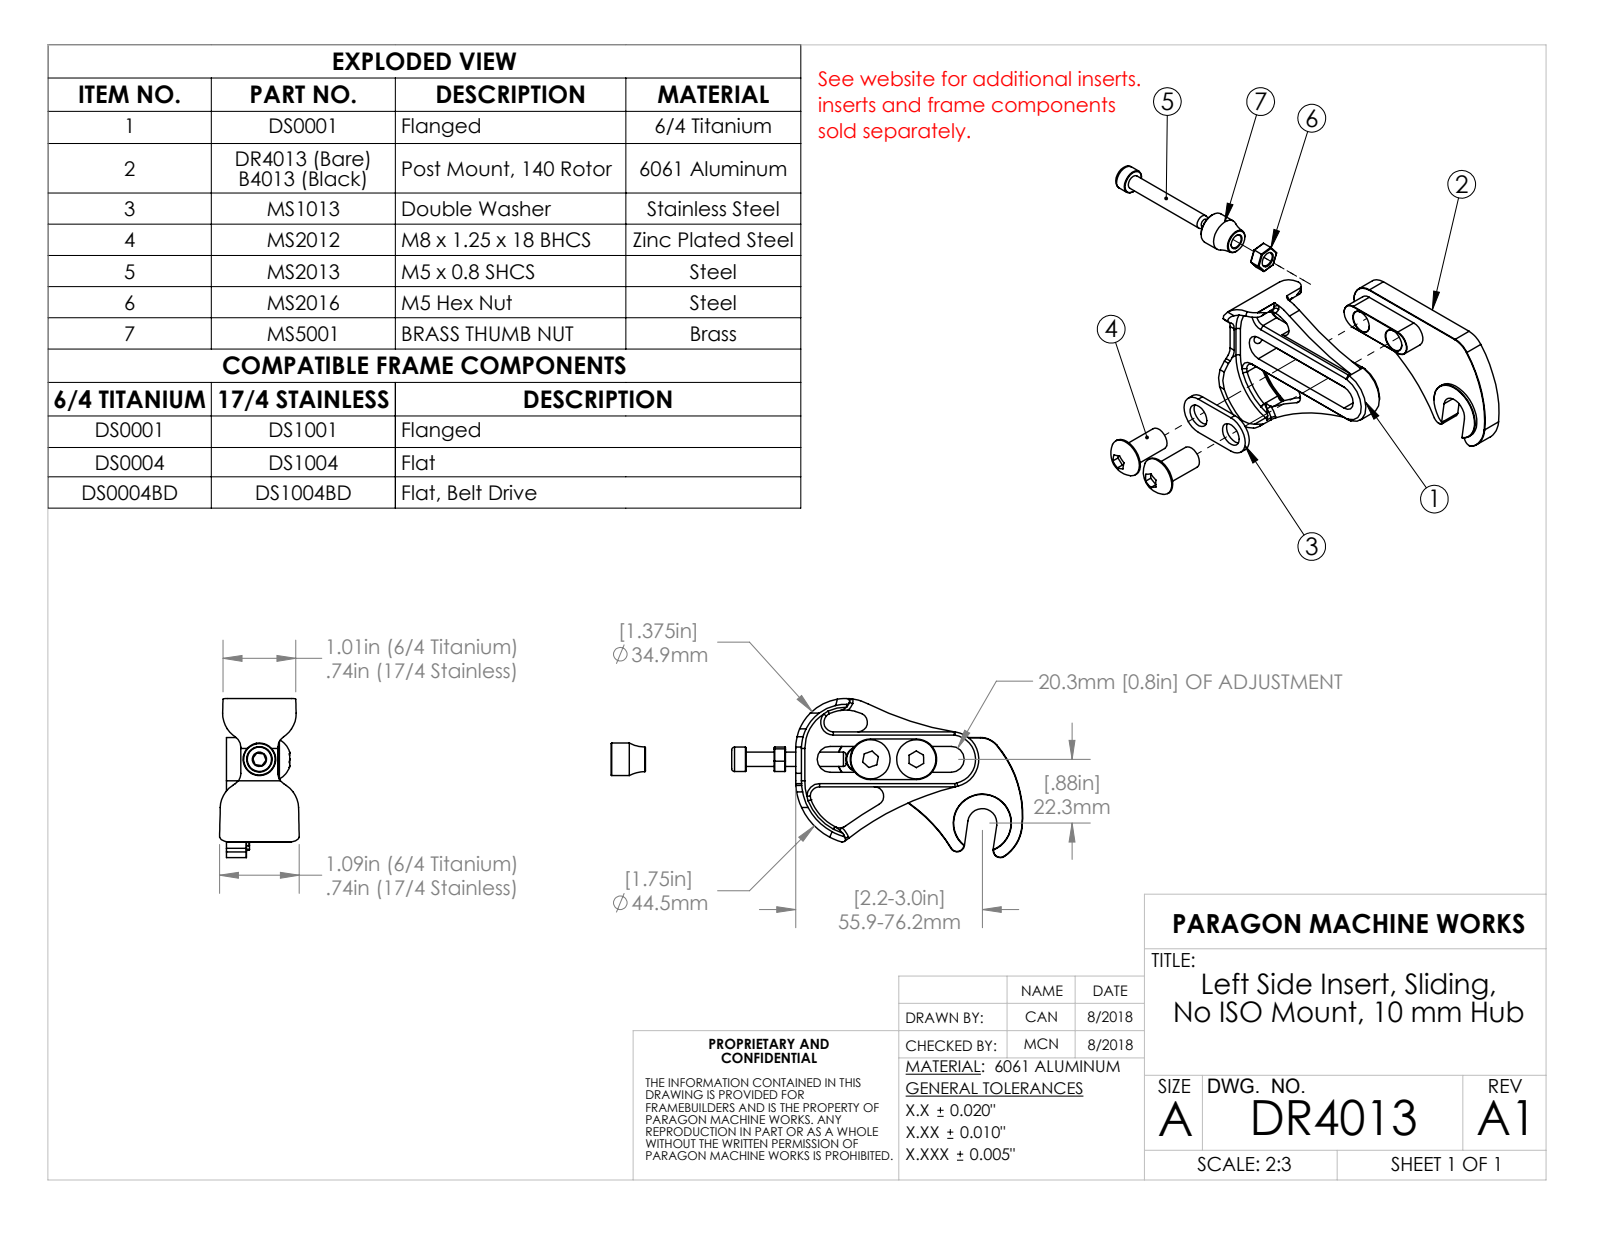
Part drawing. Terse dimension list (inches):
name: DR4013
written by: SolidWorks 2023 (AUTOMOTIVE_DESIGN)
unit: in
bodies: 1 solid, 47 faces (12 planar, 18 cylindrical, 17 other)
size: 2.358 × 2.053 × 0.59
volume: 0.733 in³; area: 8.999 in²
holes: 2× ⌀0.312
bosses: 1× ⌀0.8
rounds: 2× R0.1, 2× R0.178, 2× R0.3, 1× R0.2, 1× R0.55, 1× R1.5, 1× R2
face distances: 0.275, 0.315, 0.04, 0.478, 0.356, 0.122, 0.59, 0.4, 0.136
hole spacings: 0.63
